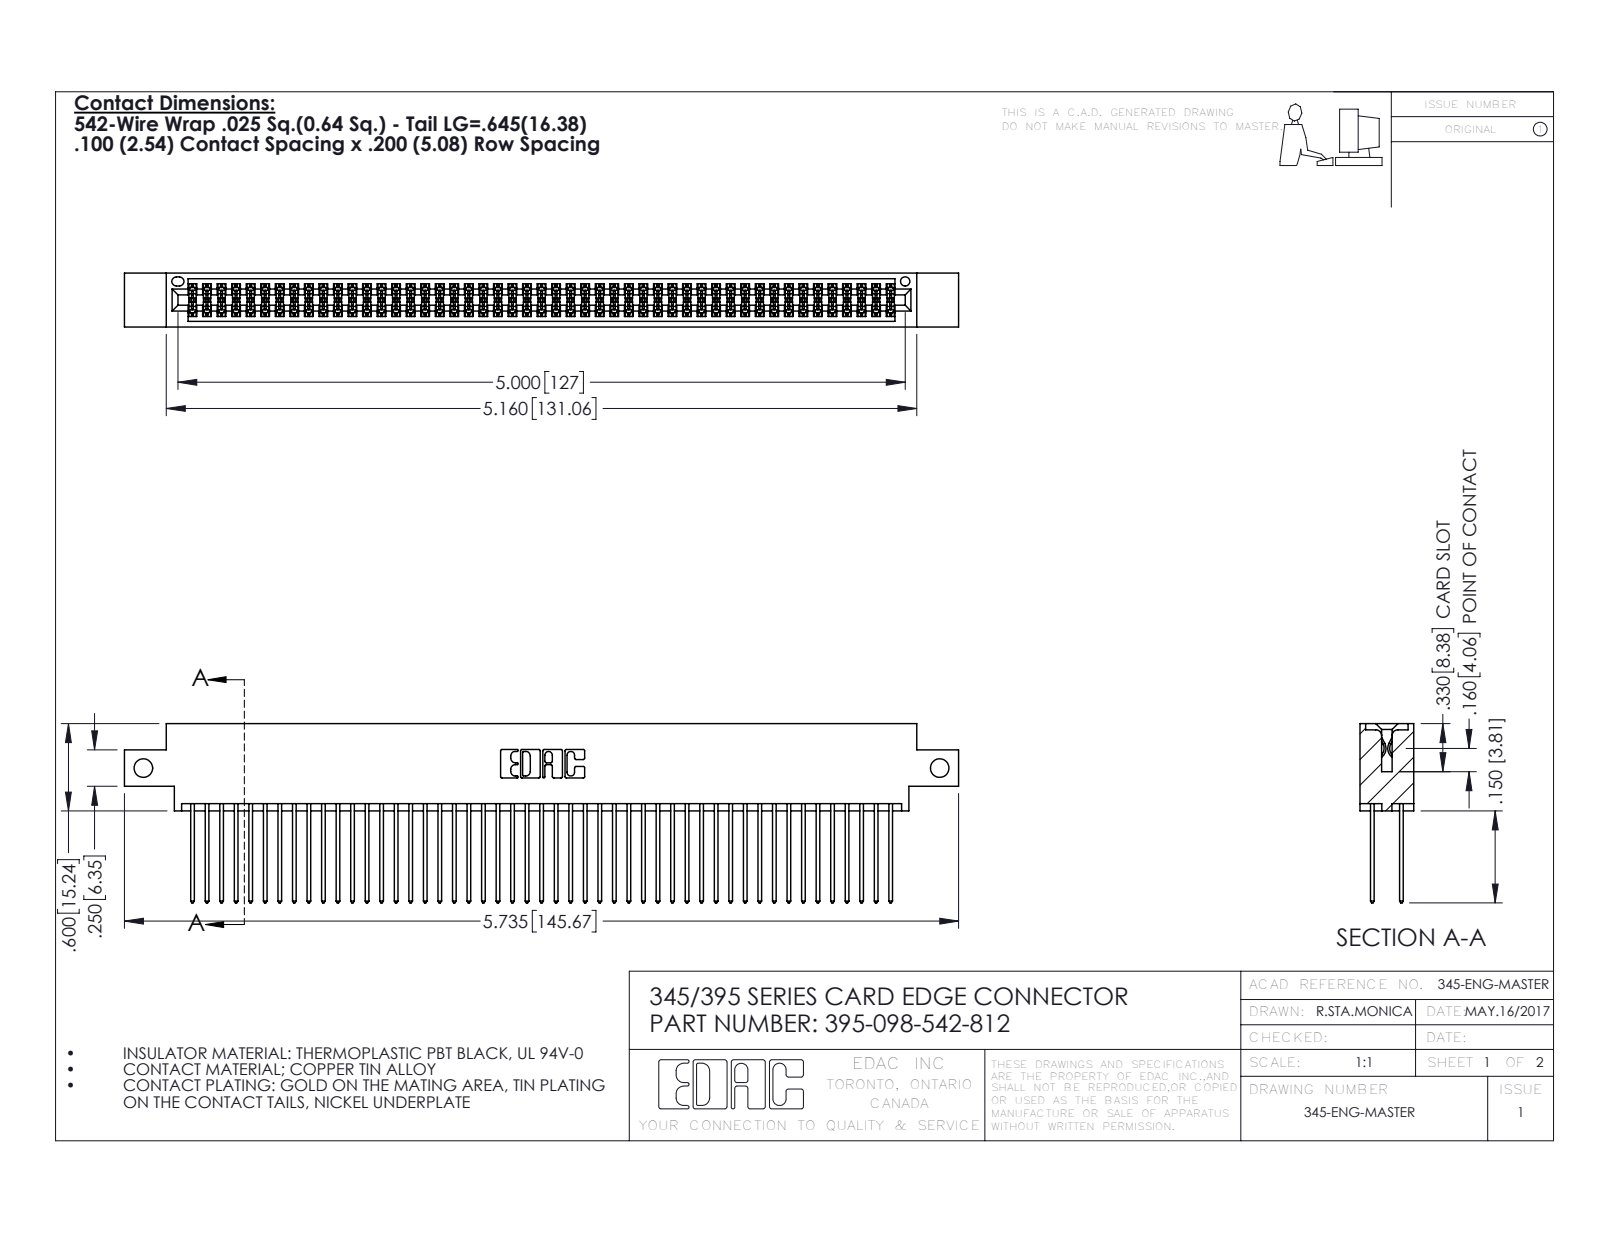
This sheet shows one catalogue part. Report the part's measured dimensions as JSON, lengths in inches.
{"part_name": "345 Part_0.170 Offset - Side Mount; 345-292-001_345-293-142; 395-098-542-812", "step_written_by": "SolidWorks 2016 (CONFIG_CONTROL_DESIGN)", "units": "inches", "bodies": {"solids": 99, "faces": 5030, "planar": 3318, "cylindrical": 1712, "other": 0}, "overall_size": [5.735, 1.232, 0.37], "volume_in3": 0.883, "surface_area_in2": 36.69, "round_holes": [[0.128, 2], [0.064, 1]], "partial_cylinders_radius": [[0.006, 147], [0.01, 98], [0.01, 22], [0.007, 6], [0.031, 6], [0.026, 3], [0.014, 2], [0.019, 2]], "face_to_face_distances": [0.072, 0.298, 0.2, 0.098, 0.272, 0.025, 0.37, 0.225, 0.175, 0.149], "hole_center_spacings": [5.475]}
